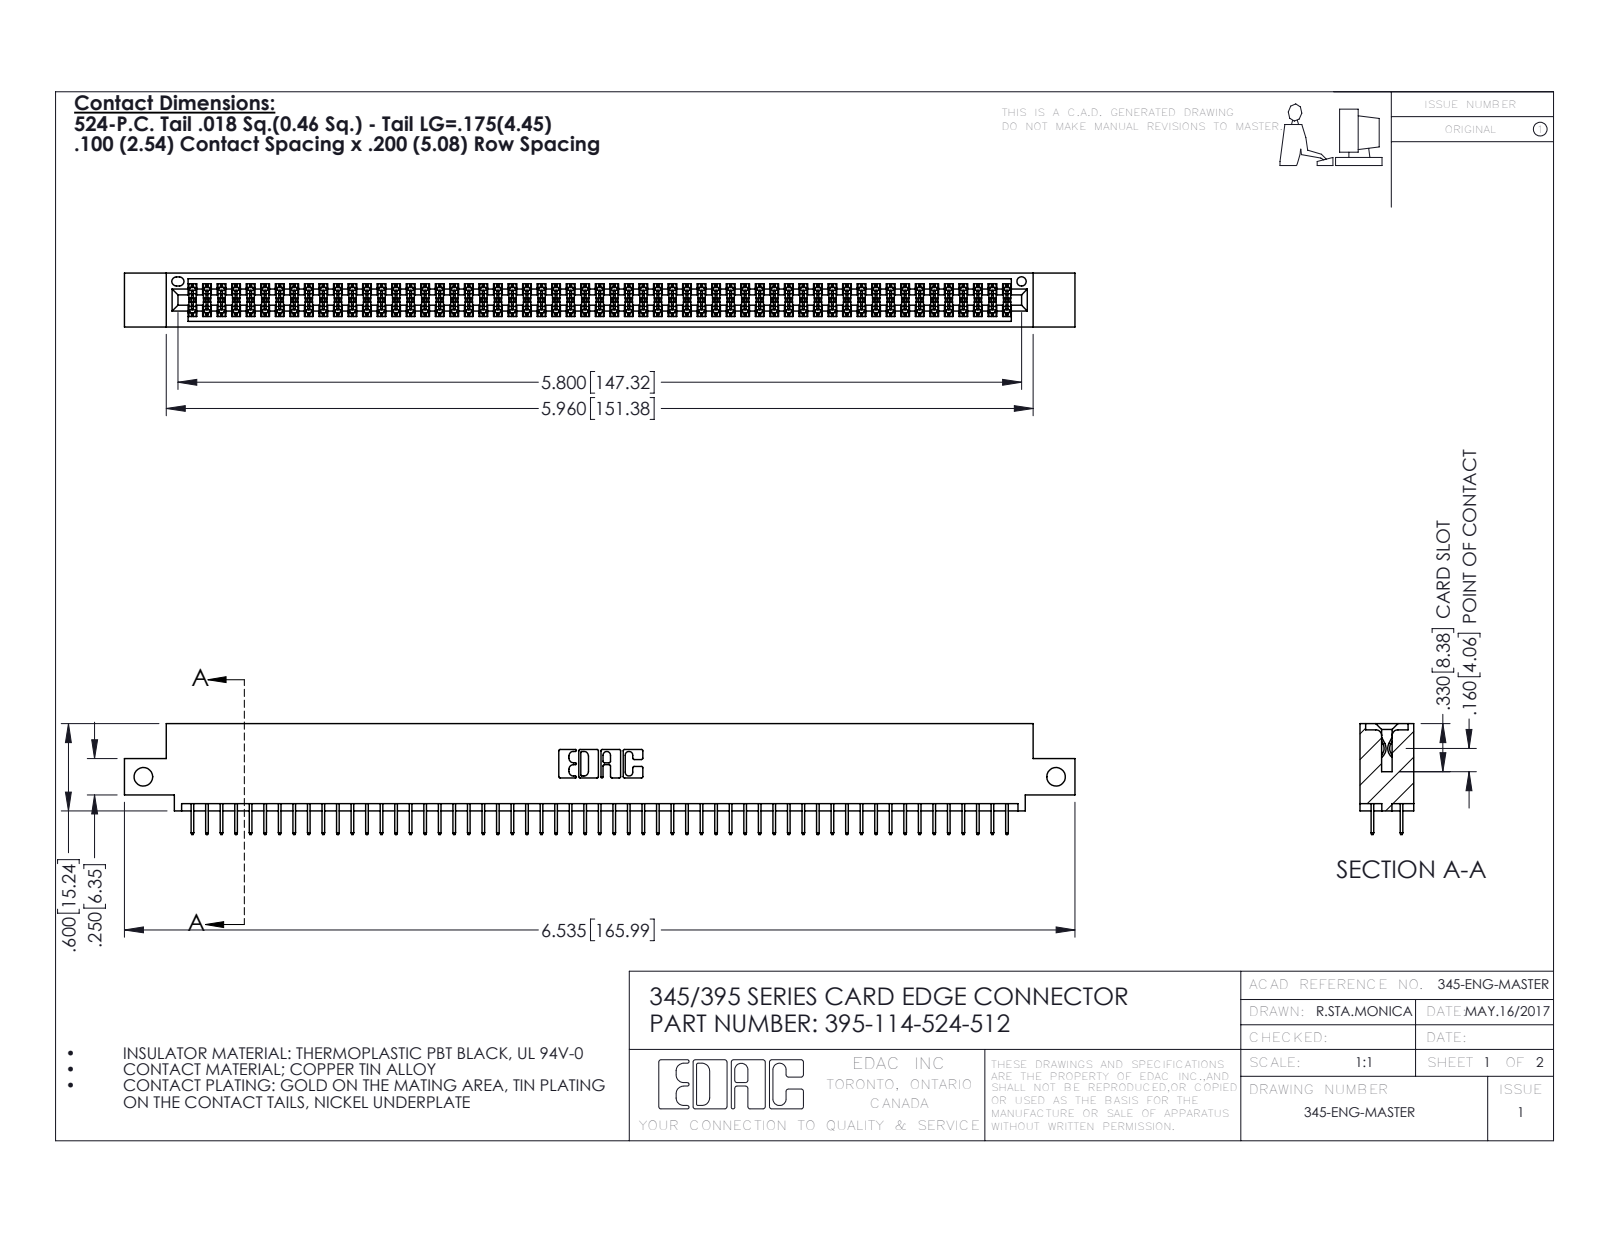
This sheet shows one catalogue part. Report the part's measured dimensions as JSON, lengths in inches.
{"part_name": "345-292-001_345-293-124; 345 Part_0.110 Offset - Side Mount; 395-114-524-512", "step_written_by": "SolidWorks 2016 (CONFIG_CONTROL_DESIGN)", "units": "inches", "bodies": {"solids": 115, "faces": 6286, "planar": 4530, "cylindrical": 1756, "other": 0}, "overall_size": [6.535, 0.762, 0.37], "volume_in3": 0.972, "surface_area_in2": 36.18, "round_holes": [[0.128, 2], [0.064, 1]], "partial_cylinders_radius": [[0.006, 171], [0.01, 22], [0.007, 6], [0.031, 6], [0.026, 3], [0.014, 2], [0.019, 2], [0.022, 2]], "face_to_face_distances": [0.072, 0.298, 0.2, 0.37, 0.098, 0.272, 0.025, 0.225, 0.072, 0.175], "hole_center_spacings": [6.275]}
